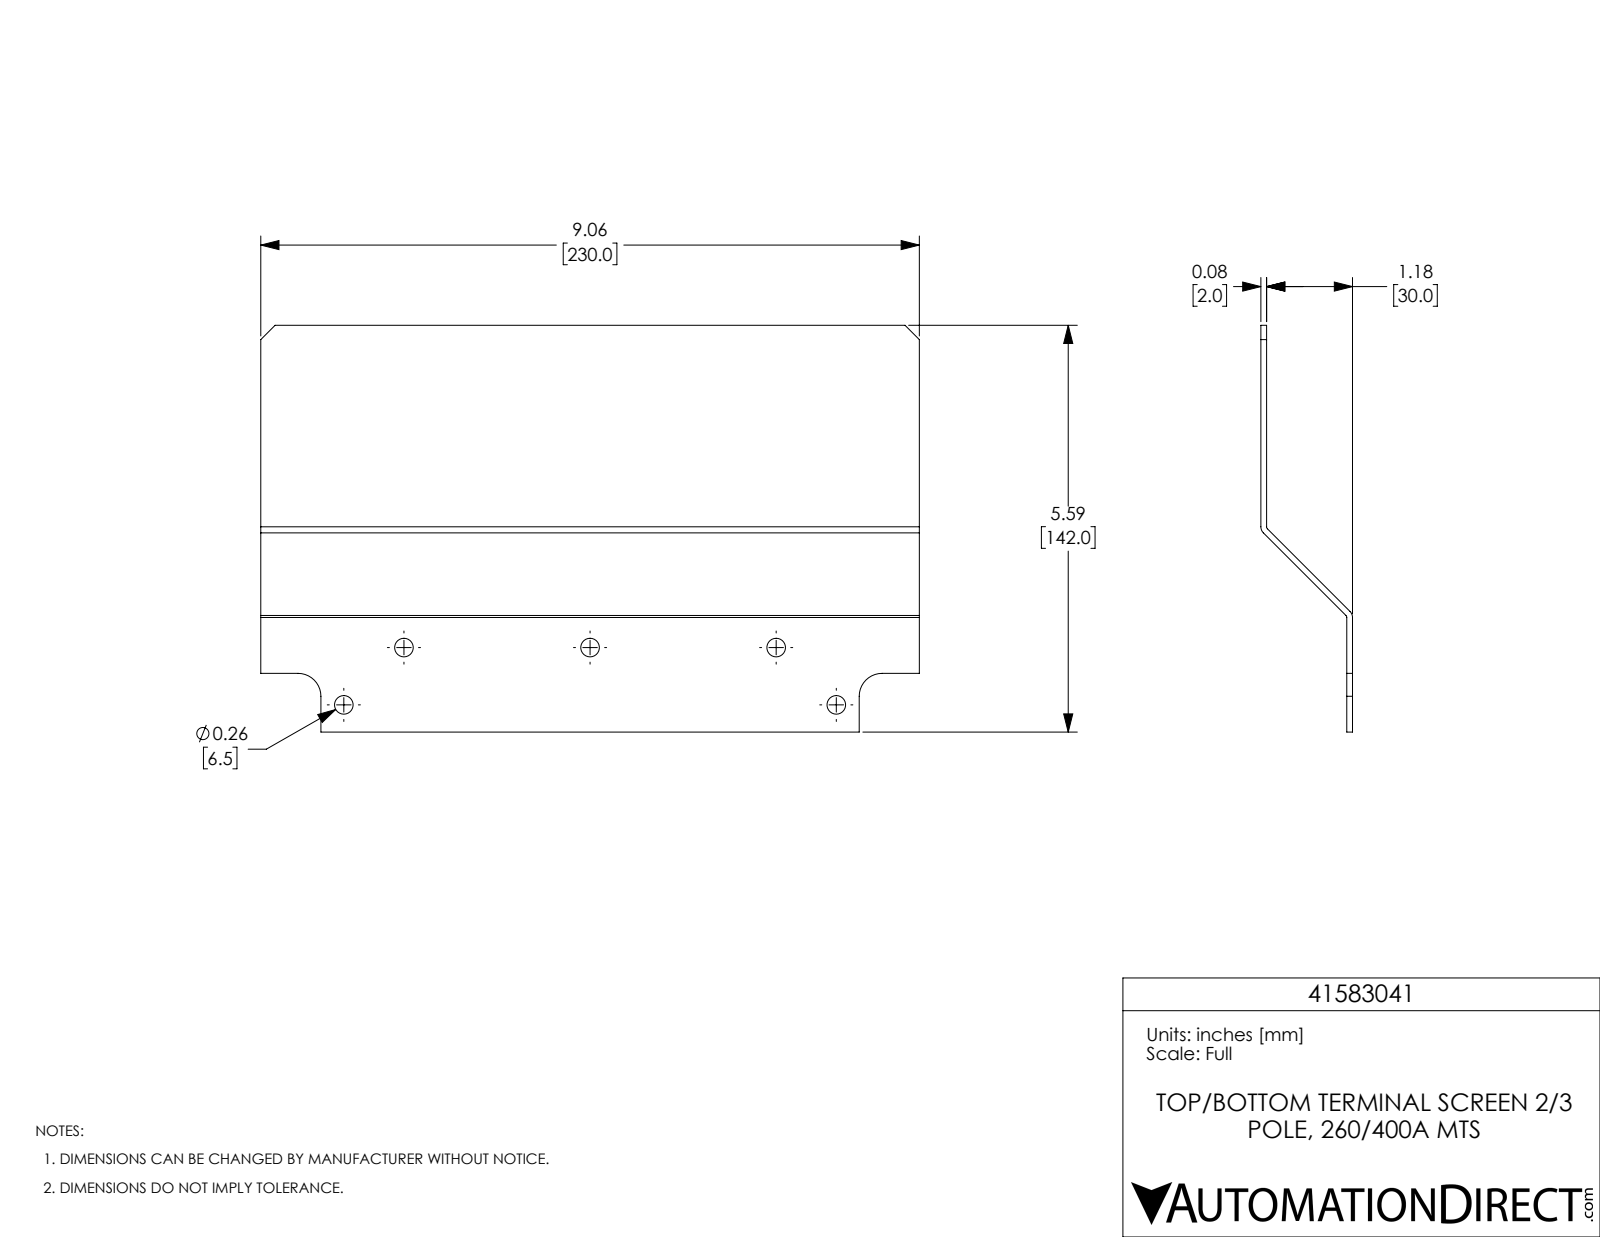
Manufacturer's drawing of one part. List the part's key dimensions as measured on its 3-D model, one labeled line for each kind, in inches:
Part name (STEP PRODUCT): 41583041
STEP written by: SolidWorks 2017 (AUTOMOTIVE_DESIGN)
Units: inches
Bodies: 1 solid, 32 faces (16 planar, 16 cylindrical, 0 other)
Overall size (bounding box): 9.055 × 5.591 × 1.26
Volume: 4.205 in³ · Surface area: 109.5 in²
Round holes (diameter × count): ⌀0.256 ×5
Partial cylindrical surfaces — rounded edges, fillets, slot ends (radius × count): R0.039 ×2, R0.118 ×2, R0.315 ×2
Main face-to-face distances: 0.079, 1.181, 1.26, 1.102, 5.591, 9.055, 0.807, 4.783, 0.827, 8.228
Hole centre spacings: 1.142, 2.559, 3.476, 5.997, 5.118, 6.772
